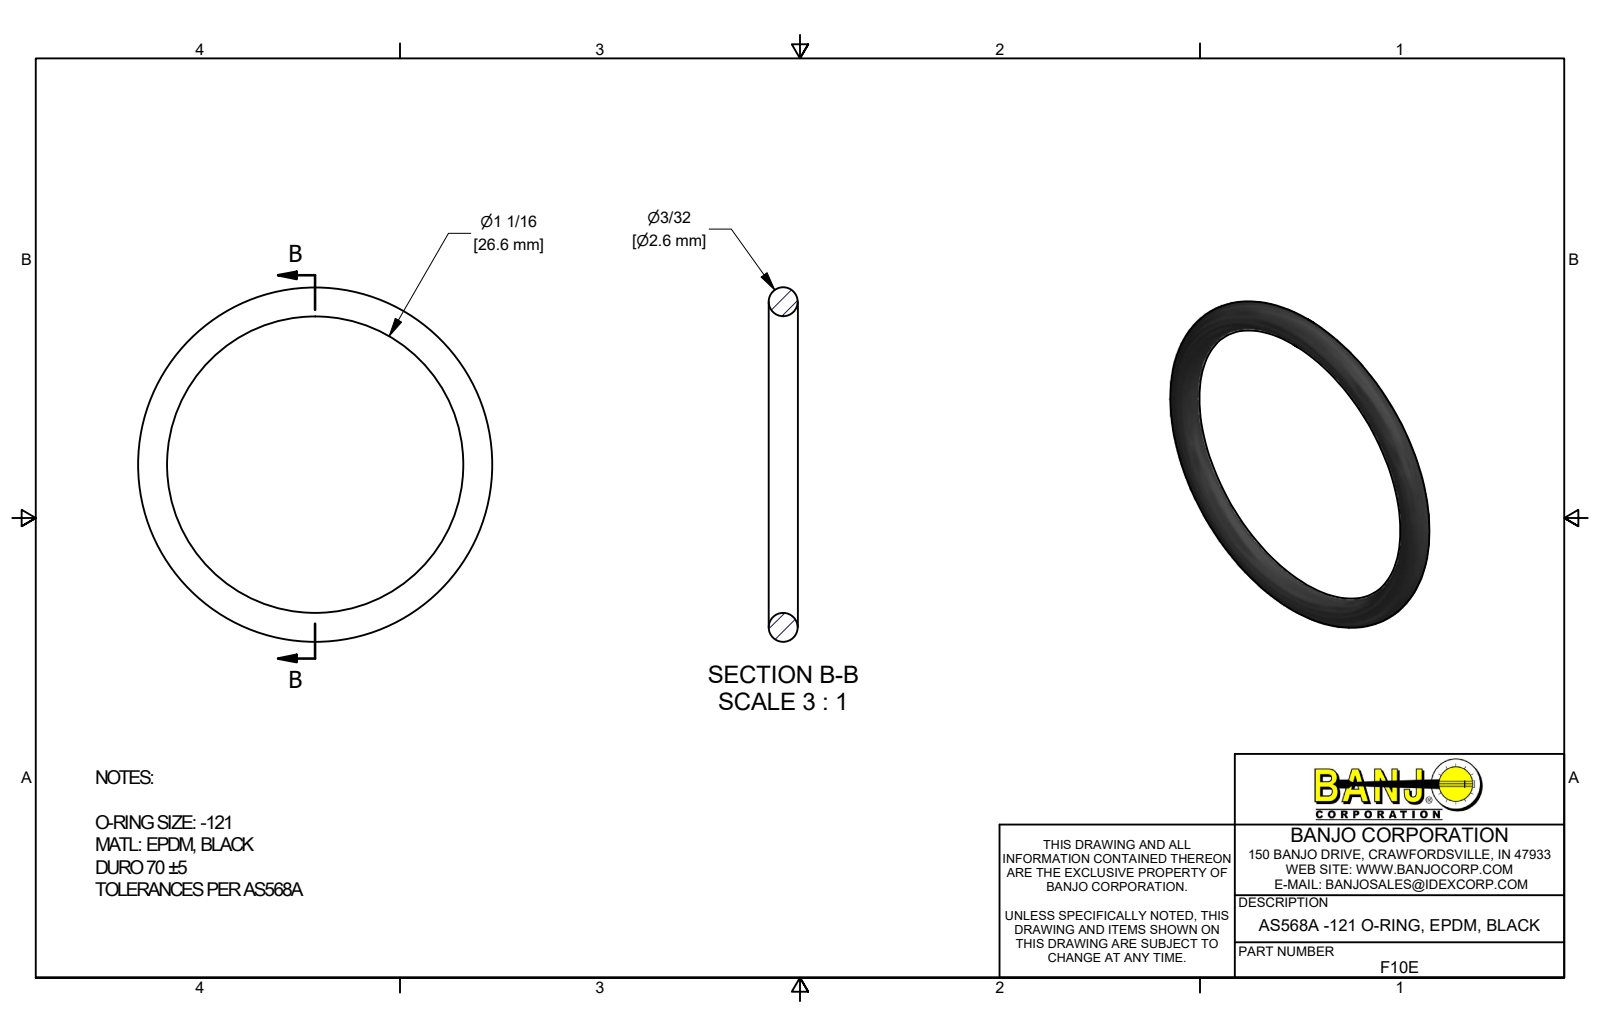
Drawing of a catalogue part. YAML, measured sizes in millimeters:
part_name: "F10E"
step_written_by: "Autodesk Inventor 2019 (AUTOMOTIVE_DESIGN)"
units: millimeters
bodies: {solids: 1, faces: 1, planar: 0, cylindrical: 0, other: 1}
overall_size: [31.9, 31.9, 2.6]
volume: 490
surface_area: 755
